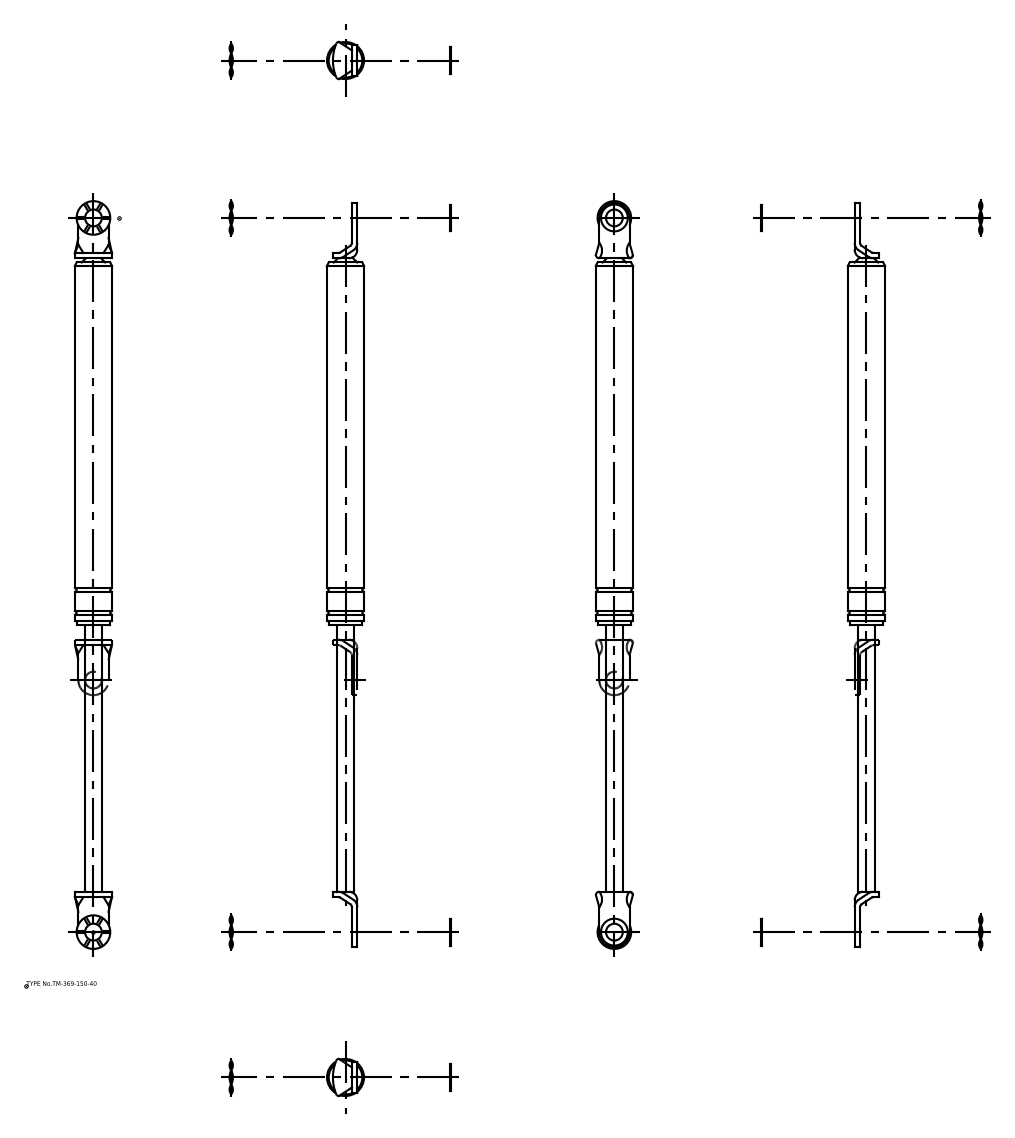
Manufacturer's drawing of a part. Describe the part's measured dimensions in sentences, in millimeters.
The part is named "ウェーブワッシャー; ワッシャー; 本体; 本体_div". Its 3-D file was written by "spGate 16.7.1 (AUTOMOTIVE_DESIGN)". It is 6 solids with 95 faces: 43 planar, 44 cylindrical and 8 other. Overall it measures 445 by 22.5 by 22.5 millimeters. Its volume is 100 100 cubic millimeters and its surface area 26 345 square millimeters. Round holes: 2 of diameter 10. Round bosses or shafts: 3 of diameter 20, 2 of diameter 16, 1 of diameter 22.5, 1 of diameter 22, 1 of diameter 10. Partial cylindrical surfaces (rounded edges, fillets, slot ends): 2 of radius 4.4, 2 of radius 5, 2 of radius 9, 1 of radius 26.32. The main face-to-face distances are 3.2, 2, 5.2, 5.7, 380.2, 3.7, 0.5, 221.2, 162.2, 383.4. The hole center spacings are 425.
